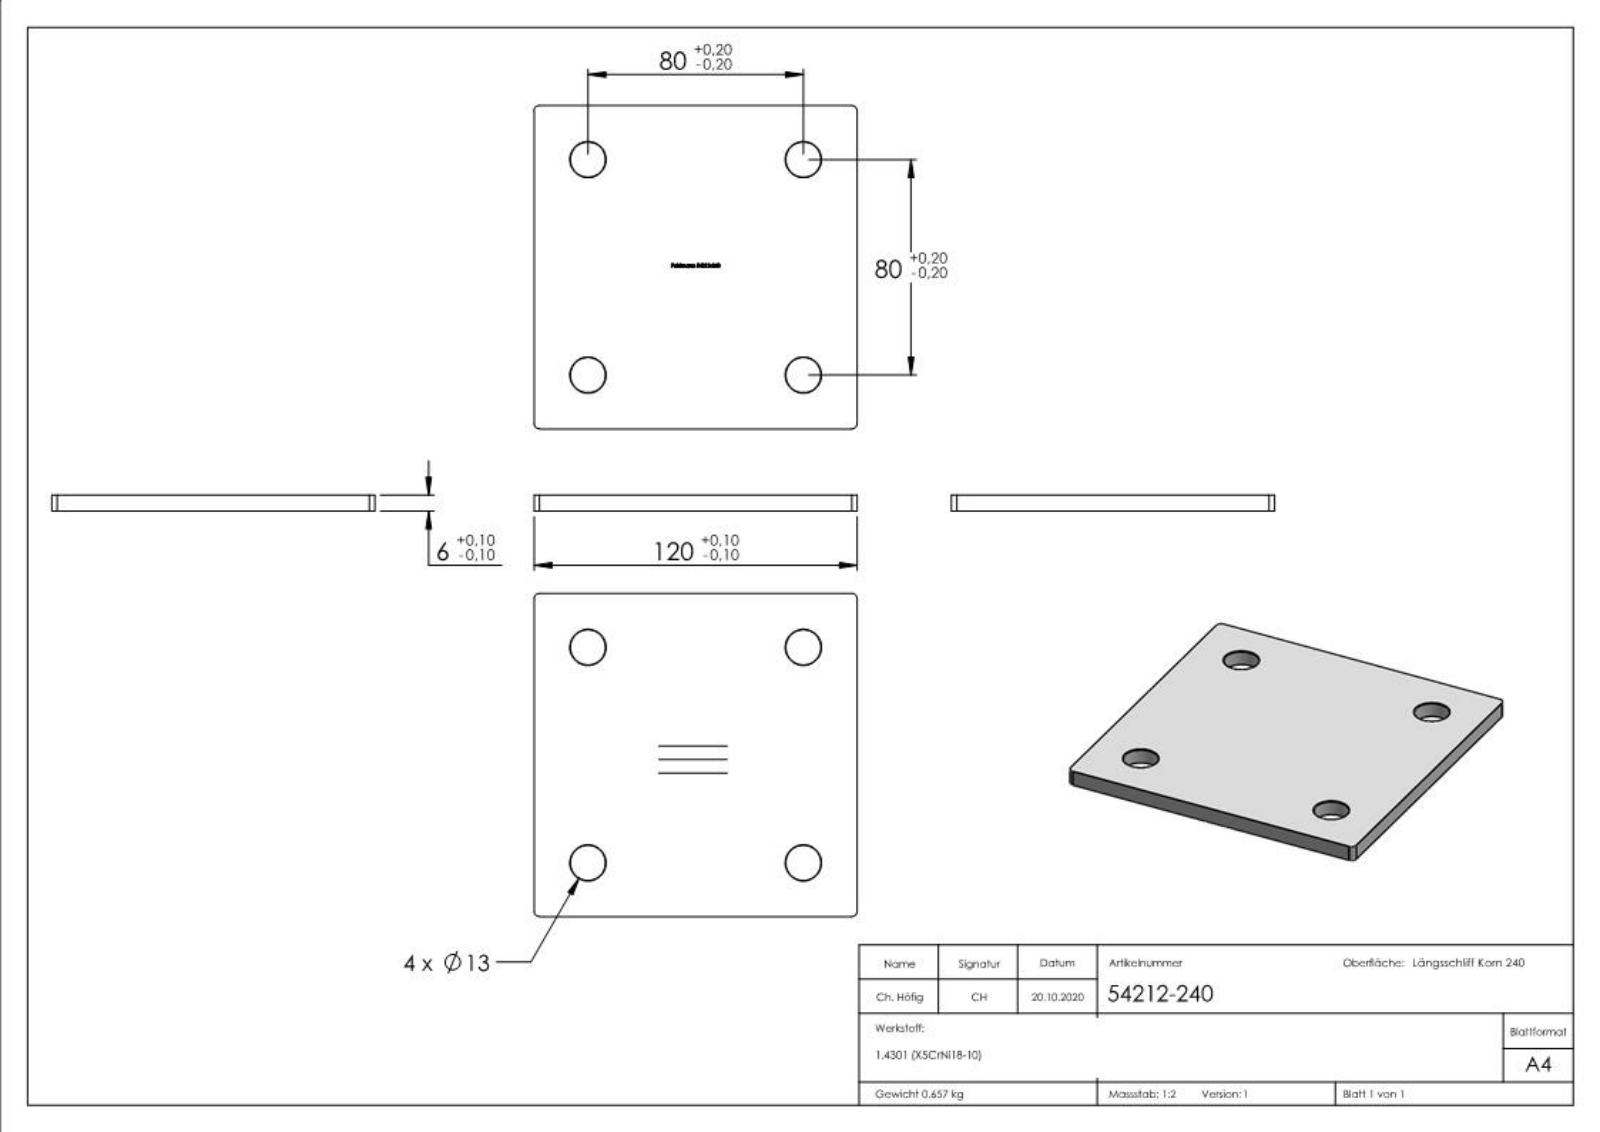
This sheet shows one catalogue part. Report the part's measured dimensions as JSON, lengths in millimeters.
{"part_name": "54212-240", "step_written_by": "SolidWorks 2018 (CONFIG_CONTROL_DESIGN)", "units": "millimeters", "bodies": {"solids": 1, "faces": 254, "planar": 143, "cylindrical": 12, "other": 99}, "overall_size": [120, 120, 6], "volume_mm3": 83183, "surface_area_mm2": 31533, "round_holes": [[13, 4]], "partial_cylinders_radius": [[2, 4]], "face_to_face_distances": [6, 120, 5.9, 60, 0.44, 0.88, 1.19, 4.7, 12.75, 14.62], "hole_center_spacings": [80, 113.14]}
